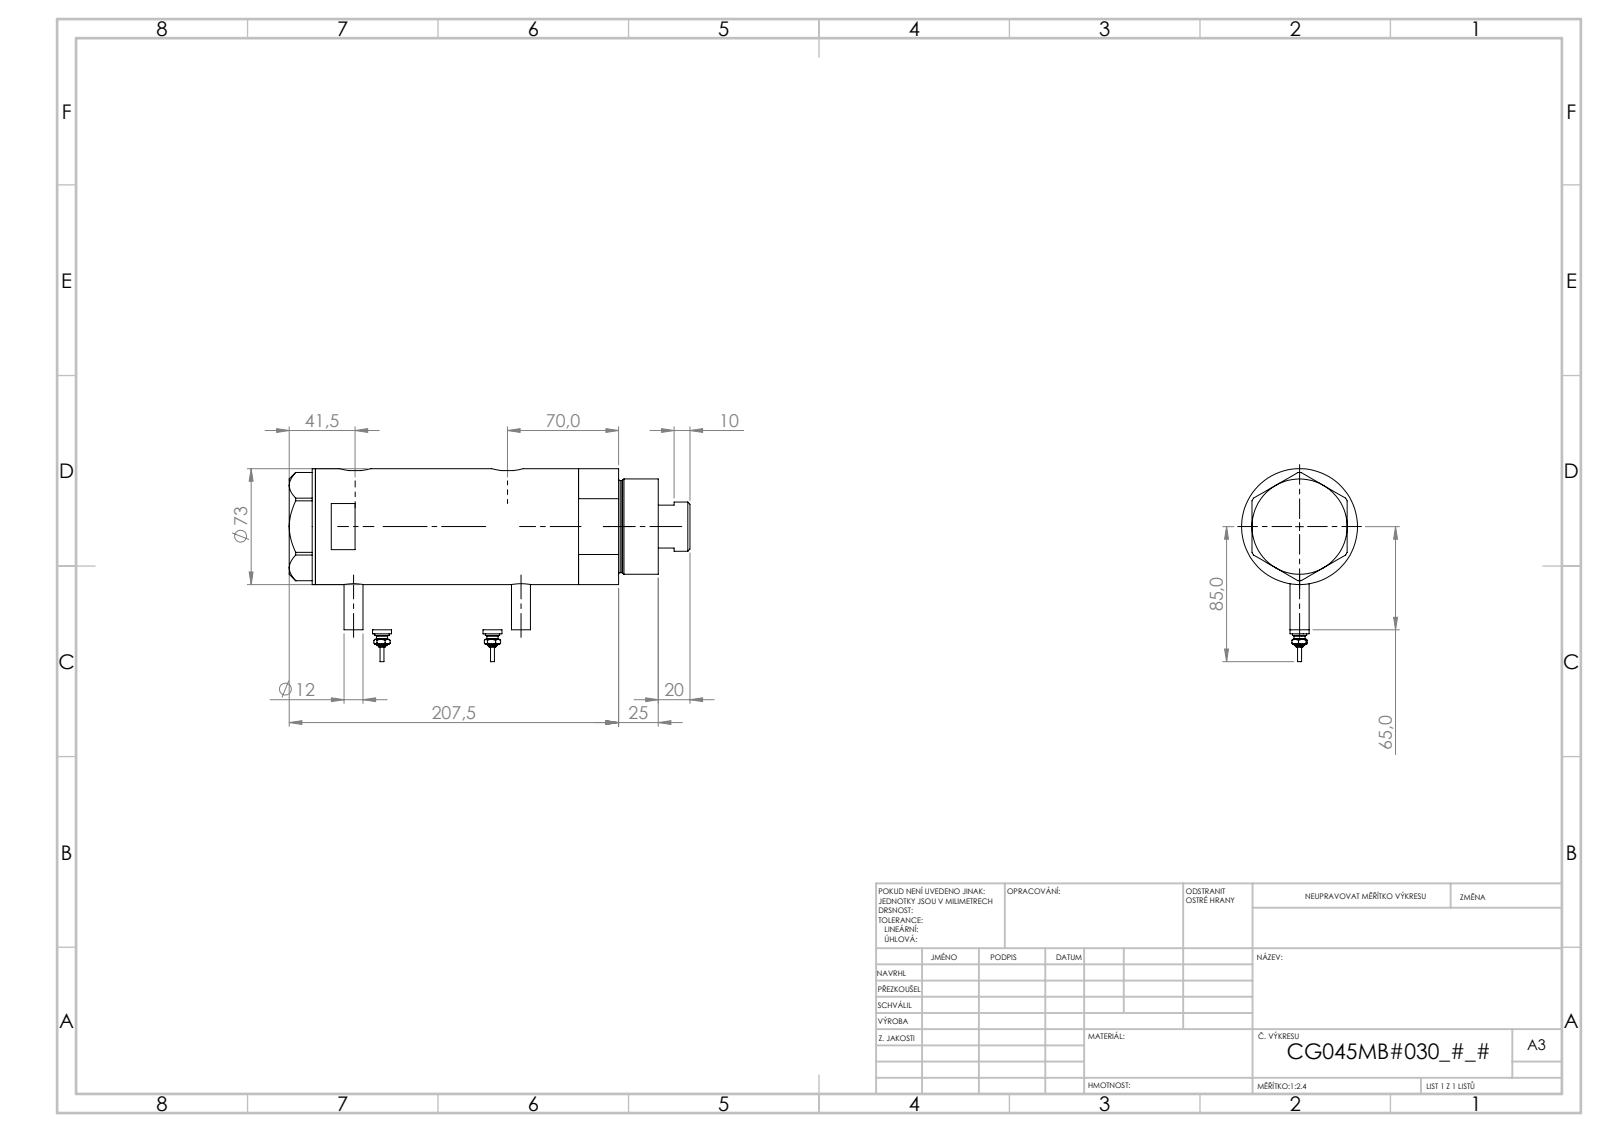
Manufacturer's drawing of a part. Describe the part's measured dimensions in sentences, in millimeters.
The part is named "V270CG_VC; V270CG_MIDDLE; V270CG_BACK; V270CG_SWITCH (+1 more)". Its 3-D file was written by "SolidWorks 2019 (CONFIG_CONTROL_DESIGN)". It is 6 solids with 231 faces: 78 planar, 79 cylindrical and 74 other. Overall it measures 221.52 by 105.3 by 73 millimeters. Its volume is 771 588 cubic millimeters and its surface area 136 024 square millimeters. Round holes: 2 of diameter 5, 2 of diameter 12.5, 2 of diameter 13.16, 1 of diameter 10.5, 1 of diameter 32, 1 of diameter 33.5, 1 of diameter 45, 1 of diameter 48, 1 of diameter 64. Round bosses or shafts: 3 of diameter 12, 2 of diameter 9, 2 of diameter 7, 2 of diameter 4.34, 2 of diameter 2.4, 1 of diameter 73, 1 of diameter 60, 1 of diameter 58. Partial cylindrical surfaces (rounded edges, fillets, slot ends): 2 of radius 10. The main face-to-face distances are 97.14, 16.5, 113.64, 185.01, 201.51, 87.87, 42.5, 26, 71.14, 159.01. The hole center spacings are 81.65, 0.99, 1, 8.5, 8.51, 72.15, 73.14, 73.15.
